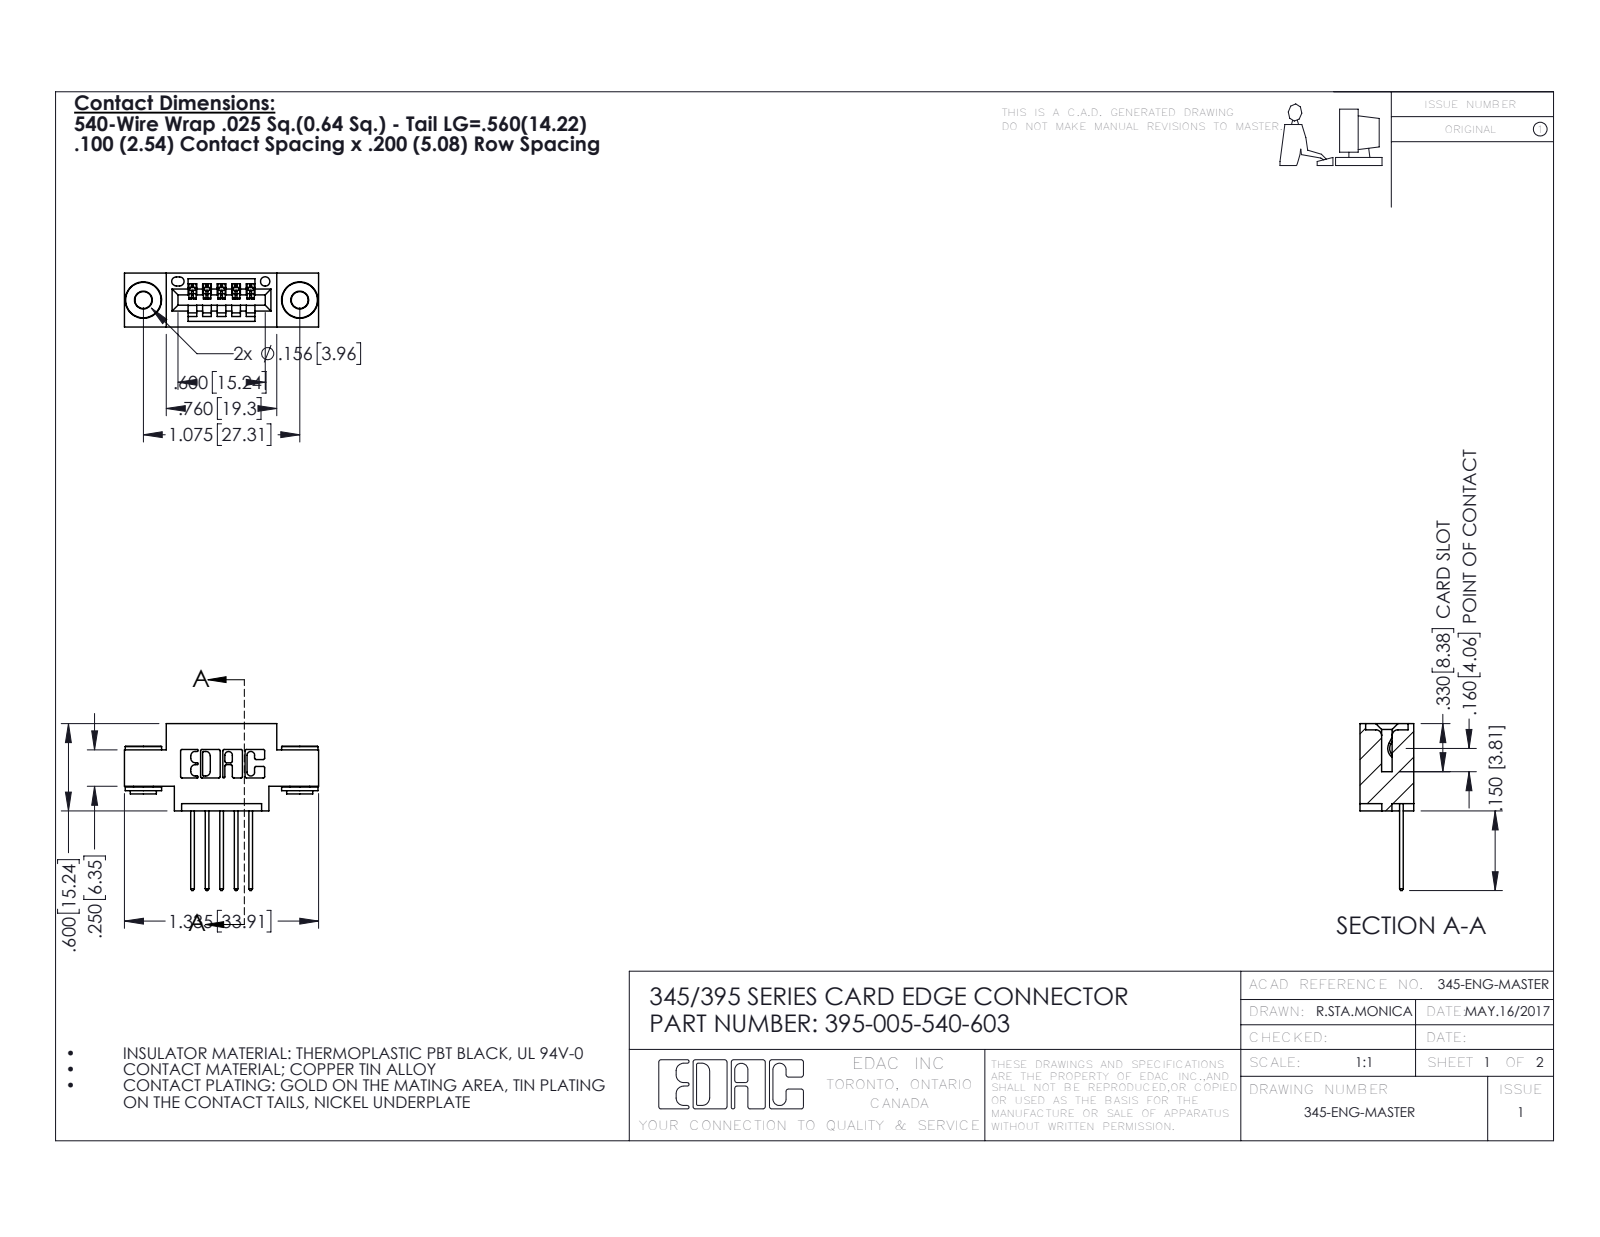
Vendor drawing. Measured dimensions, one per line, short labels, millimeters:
name: 395-005-540-603; 345-292-001_345-293-140; 345 Part_0.170 Offset - 0.156 Dia-TH; 345-250-002_345-250-002-102
written by: SolidWorks 2016 (CONFIG_CONTROL_DESIGN)
unit: mm
bodies: 8 solids, 458 faces (294 planar, 156 cylindrical, 8 other)
size: 33.9 × 29.1 × 9.4
volume: 2 830 mm³; area: 3 648 mm²
holes: 2× ⌀2.9, 2× ⌀4, 1× ⌀1.6
bosses: 2× ⌀6.4, 2× ⌀4.6, 2× ⌀3.5
rounds: 22× R0.3, 10× R0.2, 10× R0.3, 6× R0.2, 6× R0.8, 3× R0.7, 2× R0.8, 2× R1
face distances: 9.4, 5.1, 2.5, 1.8, 7.6, 0.6, 6.4, 2.5, 6.9, 1.5
hole spacings: 6.9, 21.5, 27.3
